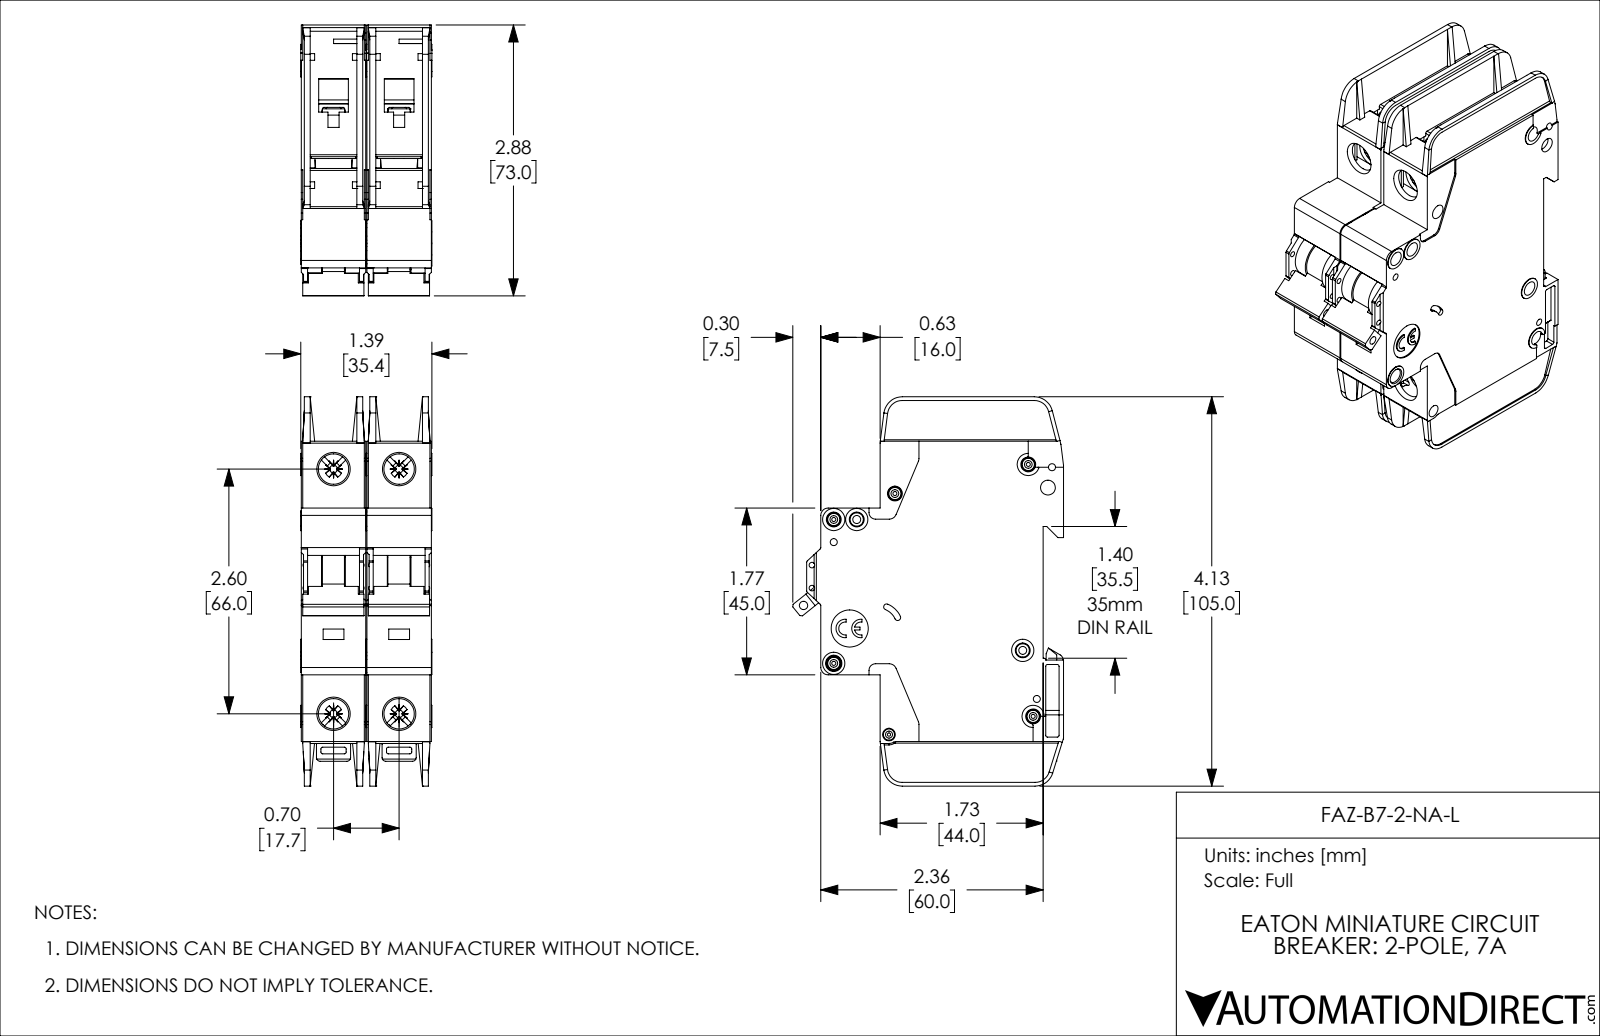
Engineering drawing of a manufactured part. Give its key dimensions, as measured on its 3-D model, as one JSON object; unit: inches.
{"part_name": "FAZ-B7-2-NA-L", "step_written_by": "SolidWorks 2019 (AUTOMOTIVE_DESIGN)", "units": "inches", "bodies": {"solids": 2, "faces": 2254, "planar": 1342, "cylindrical": 714, "other": 198}, "overall_size": [4.134, 2.876, 1.394], "volume_in3": 9.365, "surface_area_in2": 82.01, "round_holes": [[0.157, 8], [0.043, 5], [0.075, 4], [0.323, 4], [0.059, 2], [0.085, 2], [0.035, 1], [0.089, 1], [0.098, 1], [0.134, 1], [0.394, 1]], "round_bosses_or_shafts": [[0.13, 5], [0.236, 4], [0.118, 3], [0.098, 2]], "partial_cylinders_radius": [[0.02, 57], [0.016, 20], [0.039, 14], [0.079, 10], [0.043, 8], [0.008, 5], [0.197, 5], [0.01, 4]], "face_to_face_distances": [0.697, 0.047, 0.685, 0.591, 0.094, 0.638, 0.543, 1.382, 0.744, 0.65], "hole_center_spacings": [0.244, 0.537, 0.697, 0.87, 2.598, 2.69, 0.189, 0.199]}
